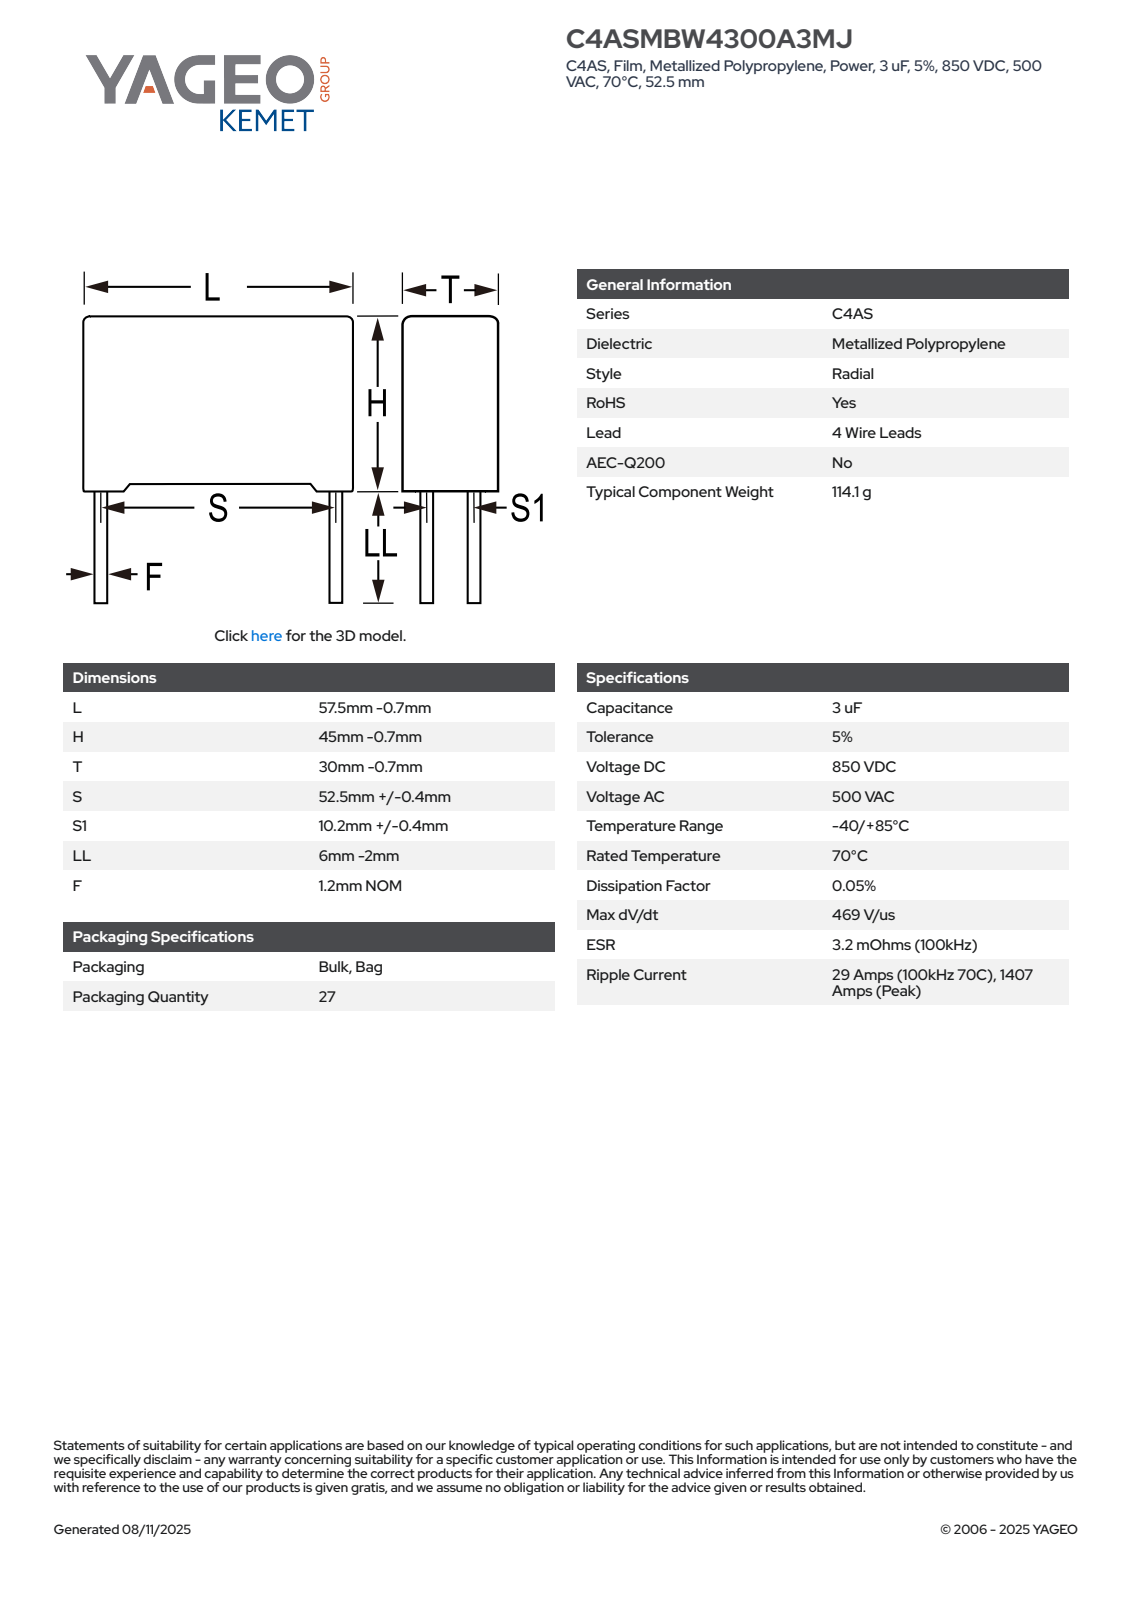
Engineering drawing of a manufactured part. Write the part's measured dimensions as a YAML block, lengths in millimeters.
part_name: "CFP_RB4_57.5X45X30_L56.8H44.3T29.3S52.5S110.2LL4F1.2"
step_written_by: "SolidWorks 2014 (AUTOMOTIVE_DESIGN)"
units: millimeters
bodies: {solids: 4, faces: 91, planar: 83, cylindrical: 8, other: 0}
overall_size: [56.8, 48.3, 29.3]
volume: 71768
surface_area: 11222
round_bosses_or_shafts:
  - {diameter: 1.2, count: 4}
face_to_face_distances: [29.3, 43, 56.8, 1.3, 44.3, 1.8, 55, 53.2, 27.5, 25.7]
